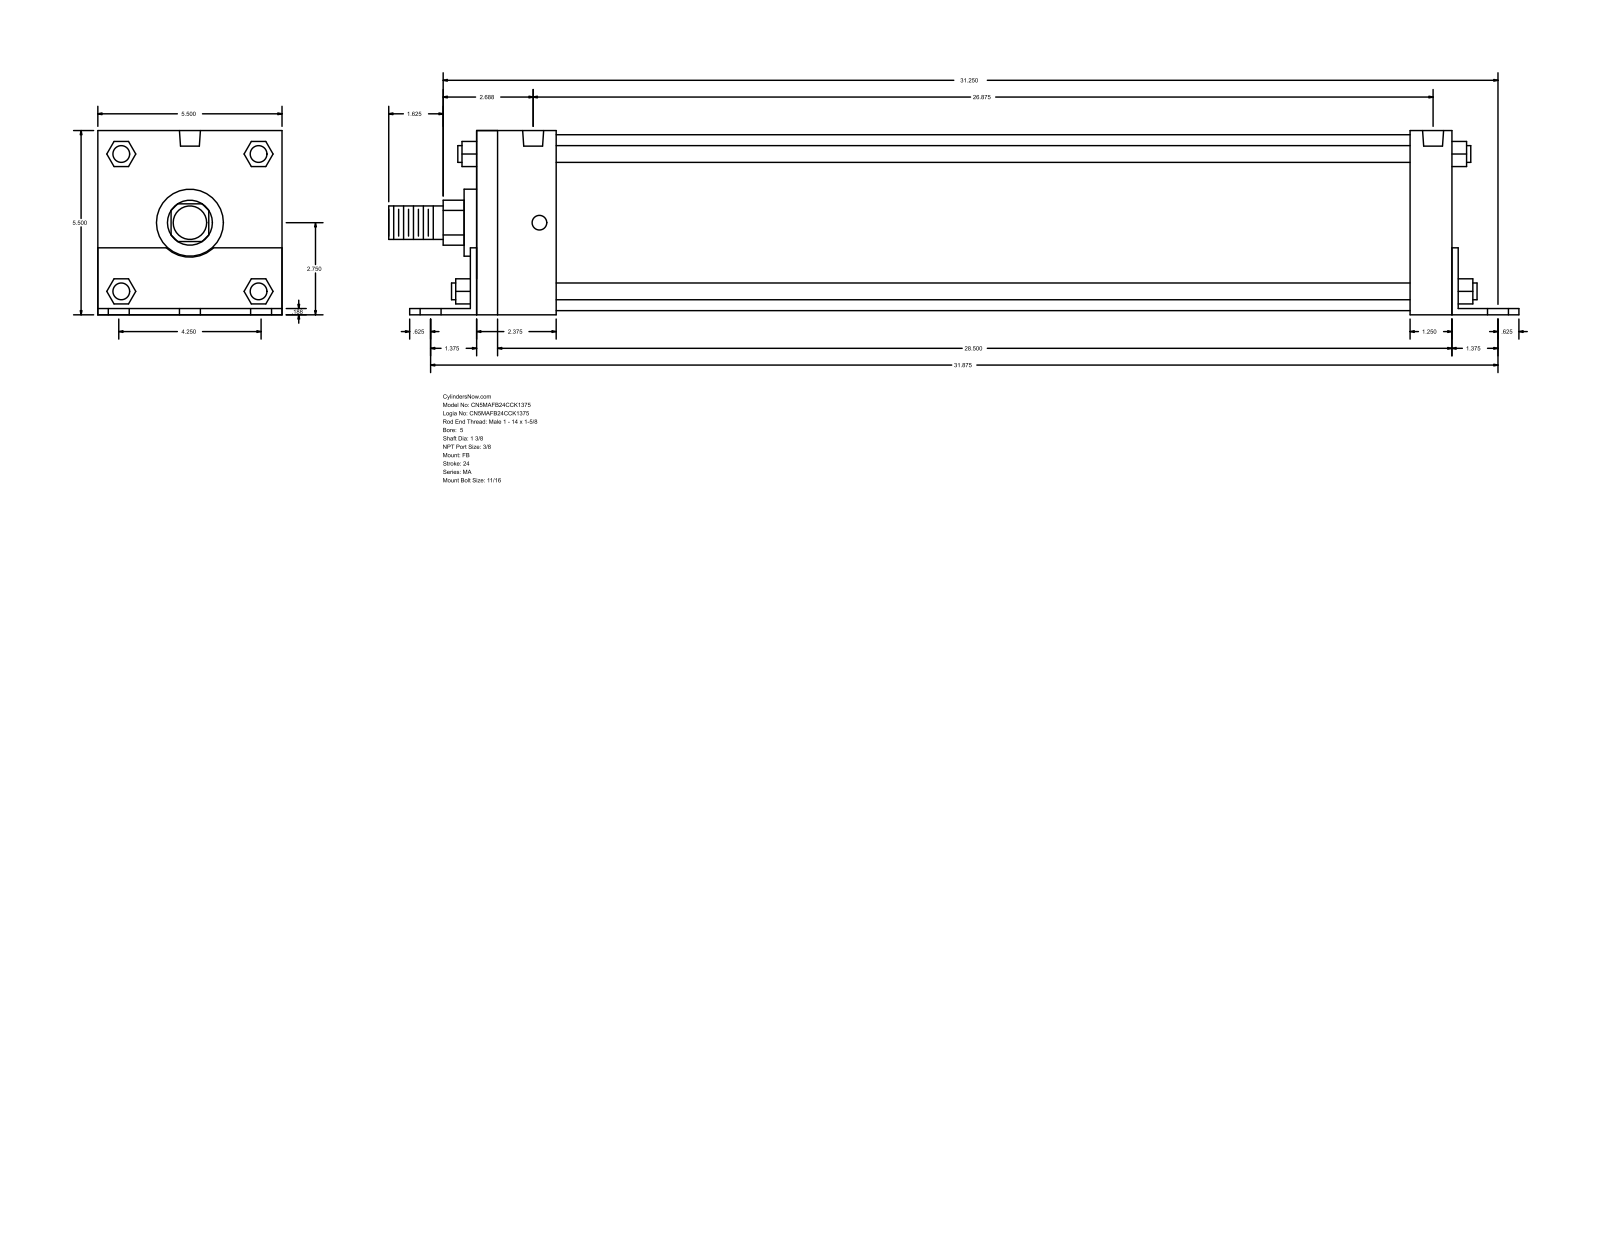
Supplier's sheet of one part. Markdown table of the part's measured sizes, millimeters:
| quantity | value |
| --- | --- |
| part name | MA_FB__0500_1.375 |
| STEP written by | GSSL Pune (CONFIG_CONTROL_DESIGN) |
| units | millimeters |
| bodies | 0 solids, 140 faces (105 planar, 35 cylindrical, 0 other) |
| overall size | 857.25 × 139.75 × 139.7 |
| round holes (diameter × count) | 17.46 × 6, 11.11 × 4, 15.93 × 2 |
| round bosses / shafts (diameter × count) | 12.7 × 4, 133.35 × 1, 50.8 × 1, 34.92 × 1, 25.4 × 1 |
| partial cylindrical surfaces (radius × count) | 17.06 × 1, 26.16 × 1 |
| main face-to-face distances | 139.7, 4.76, 139.75, 4.71, 134.99, 739.77, 4.77, 744.54, 744.53, 749.3 |
| hole center spacings | 53.98, 811.43, 809.63, 4.77, 73.04, 76.34, 94.68, 98.64 |
